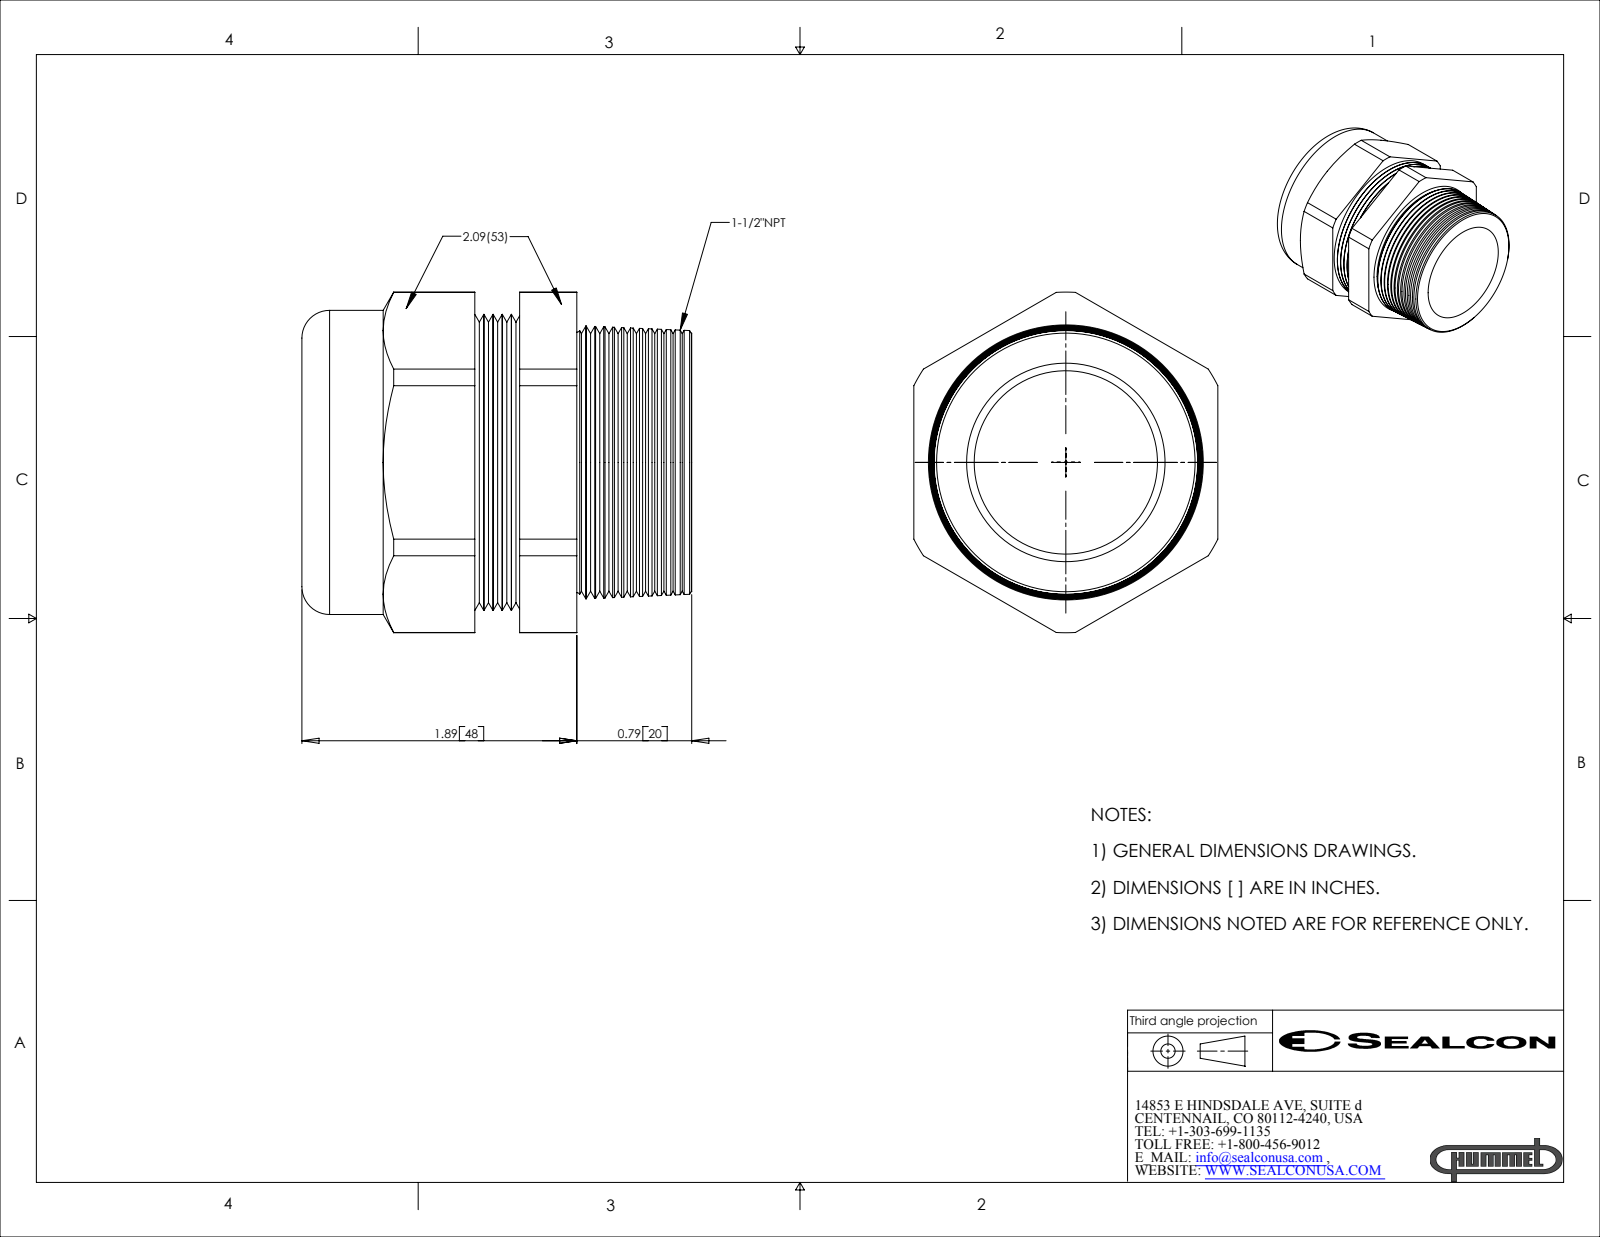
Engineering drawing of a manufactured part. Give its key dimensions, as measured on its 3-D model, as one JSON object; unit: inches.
{"part_name": "CD36NA-BK", "step_written_by": "SolidWorks 2007 (CONFIG_CONTROL_DESIGN)", "units": "inches", "bodies": {"solids": 2, "faces": 164, "planar": 20, "cylindrical": 32, "other": 112}, "overall_size": [2.68, 2.341, 2.09], "volume_in3": 5.191, "surface_area_in2": 45.47, "round_holes": [[1.26, 1], [1.598, 1]], "round_bosses_or_shafts": [[2.09, 1], [2.035, 1]], "partial_cylinders_radius": [[1.17, 1]], "face_to_face_distances": [2.09, 2.121, 1.331, 0.79, 0.539, 1.87, 2.66, 1.477, 0.938, 0.393]}
